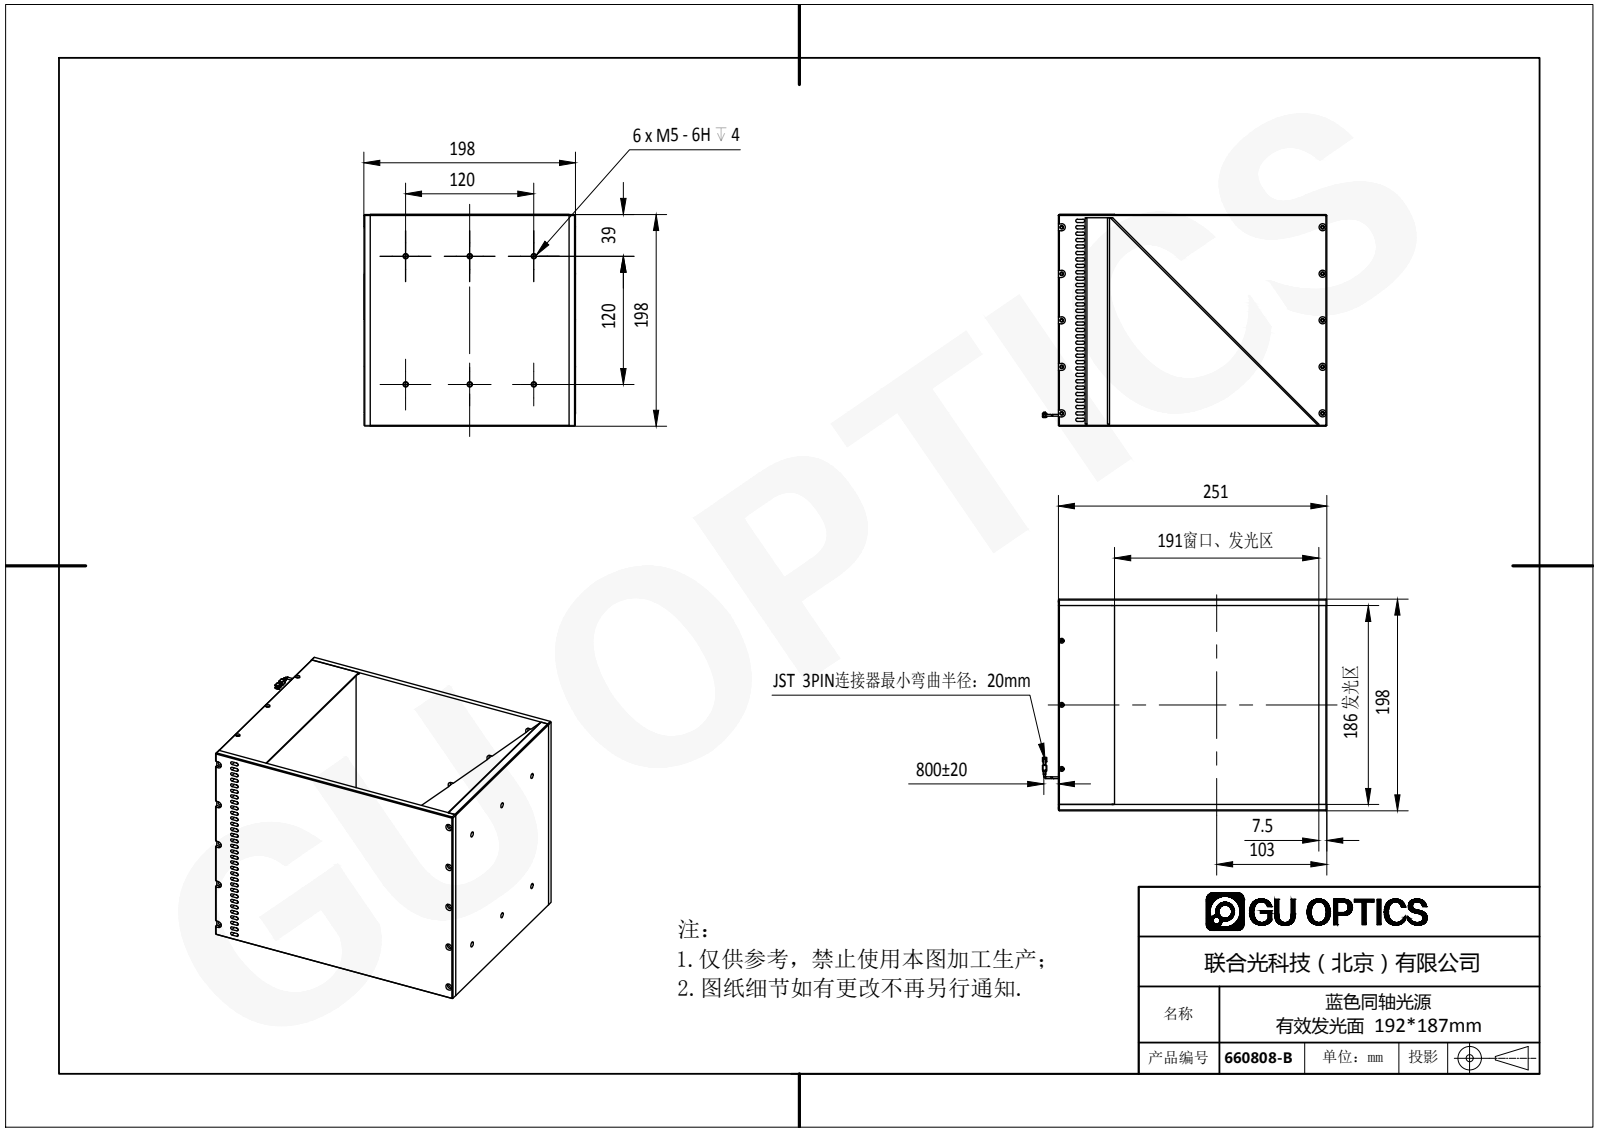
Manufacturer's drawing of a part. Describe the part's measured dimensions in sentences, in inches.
The part is named "蓝色同轴光源 有效发光面 192187mm". Its 3-D file was written by "SolidWorks 2016 (AUTOMOTIVE_DESIGN)". It is 21 solids with 4677 faces: 3722 planar, 818 cylindrical and 137 other. Overall it measures 10.472 by 7.803 by 7.795 inches. Its volume is 82.02 cubic inches and its surface area 1 219 square inches. Round holes: 26 of diameter 0.098, 10 of diameter 0.118, 10 of diameter 0.134, 6 of diameter 0.165, 6 of diameter 0.197, 5 of diameter 0.256, 5 of diameter 0.276, 4 of diameter 1.496, 4 of diameter 1.89, 4 of diameter 2.283, 3 of diameter 0.063, 3 of diameter 0.079. Round bosses or shafts: 4 of diameter 2.008, 4 of diameter 1.614, 2 of diameter 0.069. Partial cylindrical surfaces (rounded edges, fillets, slot ends): 64 of radius 0.059, 32 of radius 0.069, 32 of radius 0.069, 32 of radius 0.07, 9 of radius 0.043, 8 of radius 0.02, 8 of radius 0.035, 8 of radius 0.041. The main face-to-face distances are 7.795, 7.559, 0.236, 0.079, 0.059, 7.717, 7.323, 8.091, 0.063, 8.012. The hole center spacings are 1.969, 1.392, 9.606, 2.784, 4.054, 3.425, 3.543, 3.937.
